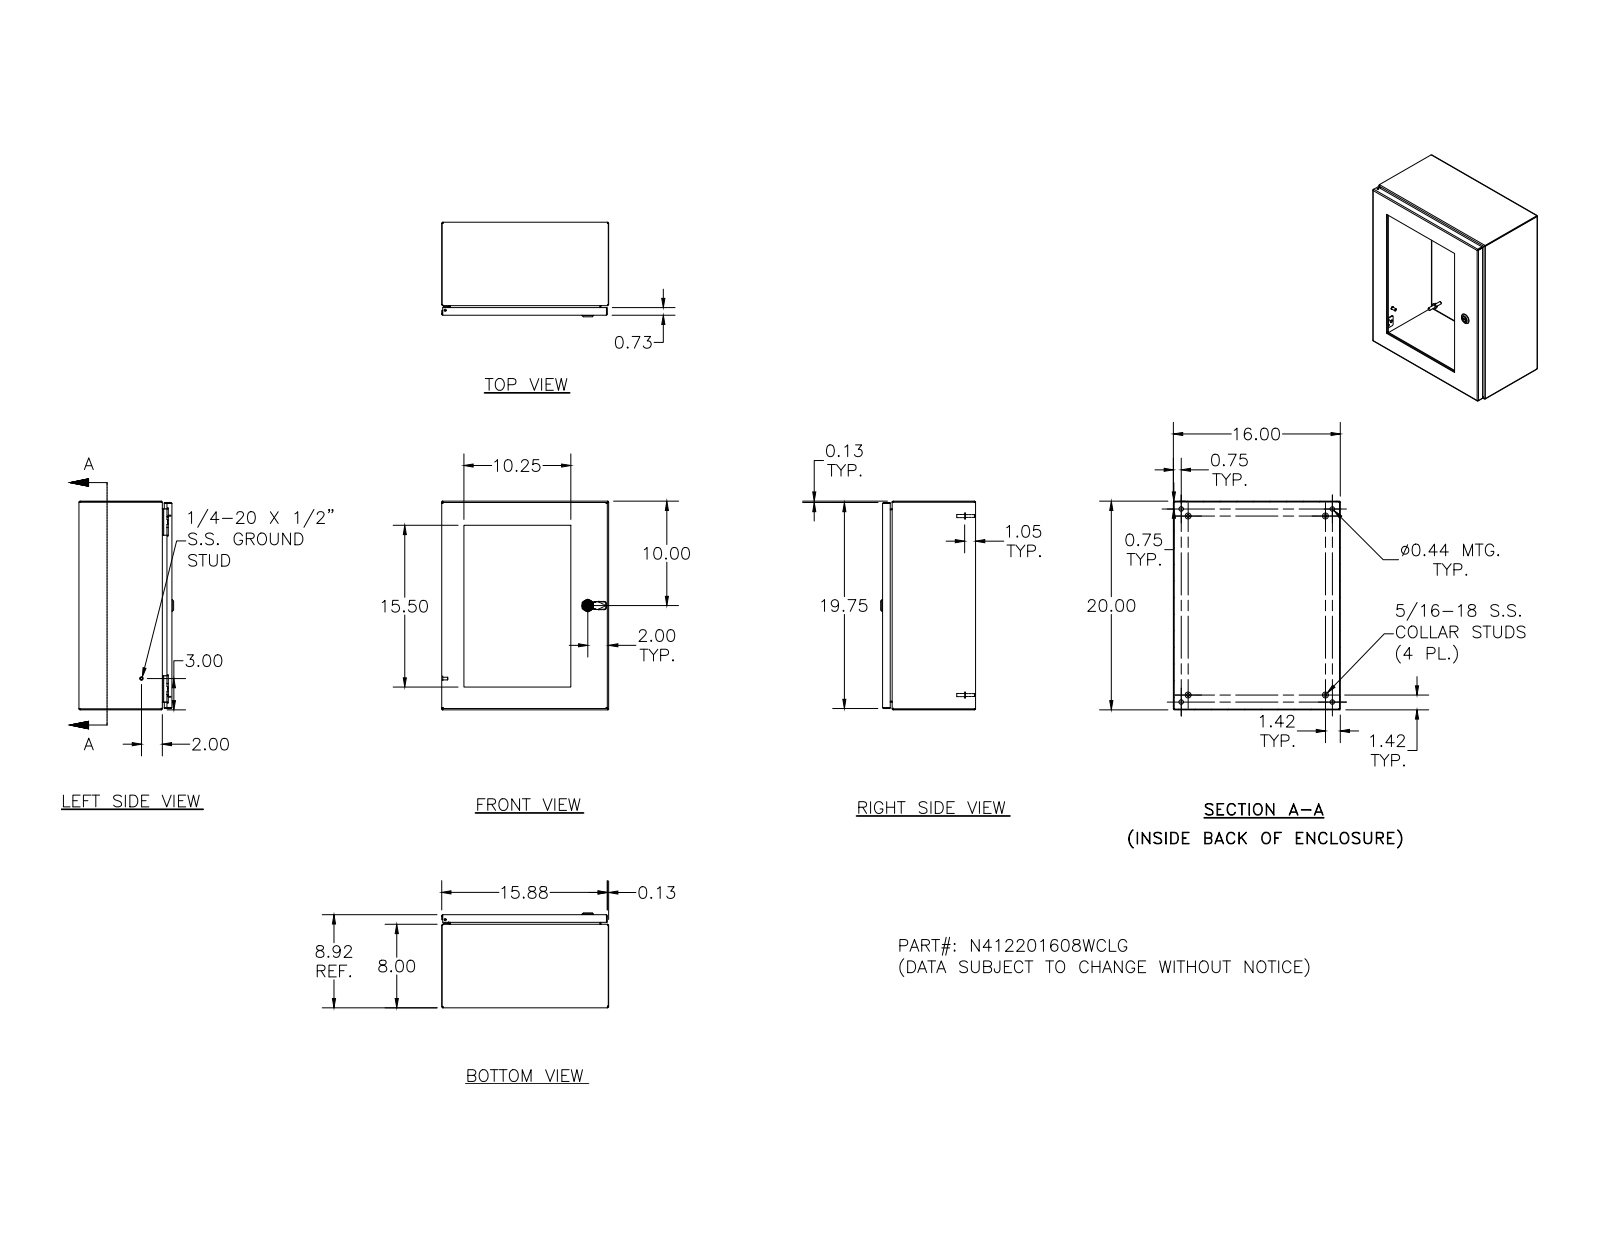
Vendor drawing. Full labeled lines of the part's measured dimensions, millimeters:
Part name (STEP PRODUCT): N412201608WCLG
STEP written by: SolidWorks 2018 (AUTOMOTIVE_DESIGN)
Units: millimetres
Bodies: 65 solids, 1955 faces (731 planar, 609 cylindrical, 615 other)
Overall size (bounding box): 508 × 406.4 × 230.5
Volume: 2 299 000 mm³ · Surface area: 1 908 000 mm²
Round holes (diameter × count): ⌀4 ×16, ⌀7.1 ×14, ⌀4.8 ×5, ⌀2.4 ×4, ⌀3.9 ×4, ⌀4.2 ×4, ⌀4.4 ×4, ⌀11.1 ×4, ⌀4.7 ×1, ⌀5 ×1, ⌀8 ×1, ⌀10 ×1
Round bosses / shafts (diameter × count): ⌀8.6 ×14, ⌀4.8 ×14, ⌀6.4 ×10, ⌀14.3 ×4, ⌀9.1 ×4, ⌀8.1 ×4, ⌀7.6 ×4, ⌀7 ×4
Partial cylindrical surfaces — rounded edges, fillets, slot ends (radius × count): R0.8 ×34, R0.3 ×30, R1.3 ×26, R2.7 ×24, R0.4 ×18, R3.2 ×16, R0.5 ×13, R0.8 ×8
Main face-to-face distances: 1.9, 224.6, 222.7, 404.5, 506.1, 6.4, 218.3, 216.4, 402.6, 406.4
Hole centre spacings: 101.6, 203.2, 309.3, 406.4, 158, 218.1, 254.9, 292.1
